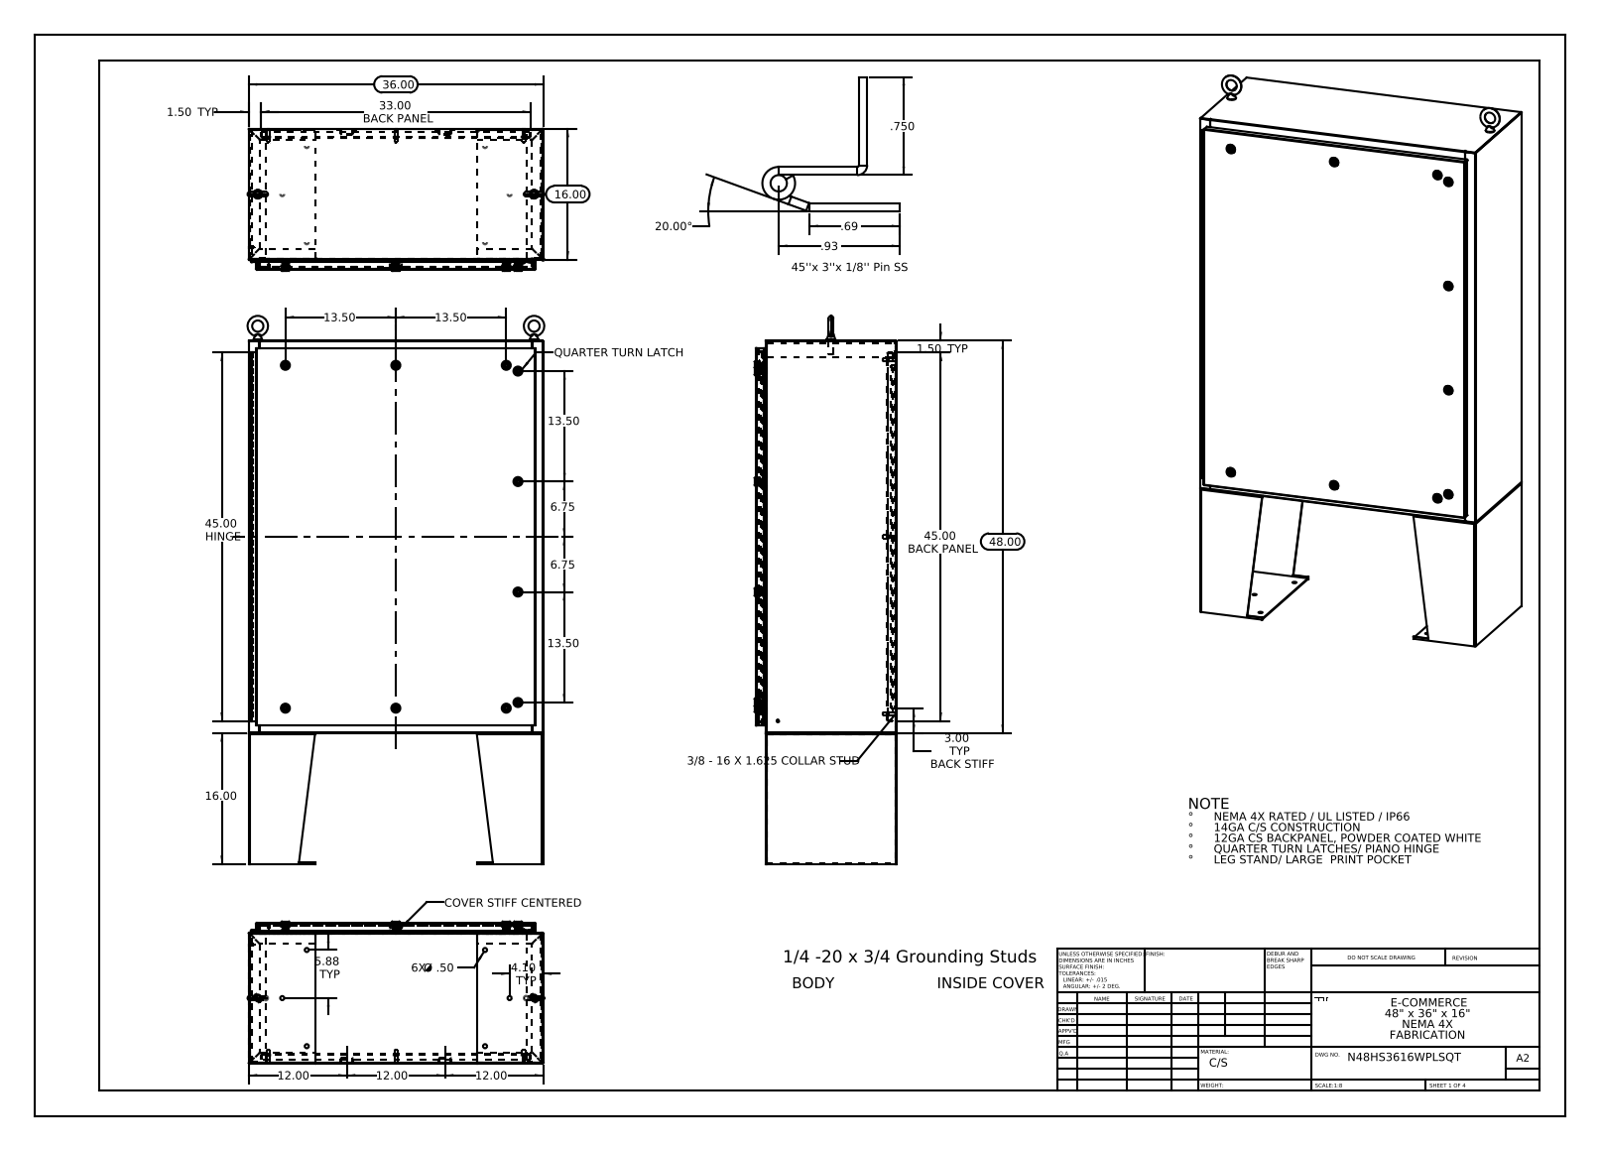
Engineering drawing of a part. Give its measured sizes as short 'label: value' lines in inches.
name: N48HS3616SSWPLSQT SD-LSK - Base; N48HS3616SSWPLSQT Hinge Enclosure Side2; N48HS3616SSWPLSQT Bottom; N48HS3616SSWPLSQT Backpanel (+8 more)
written by: SolidWorks 2013 (CONFIG_CONTROL_DESIGN)
unit: in
bodies: 34 solids, 2043 faces (1041 planar, 822 cylindrical, 180 other)
size: 67 × 36.271 × 17.201
volume: 845 in³; area: 20 263 in²
holes: 14× ⌀0.5, 6× ⌀0.25, 4× ⌀0.75, 1× ⌀0.125, 1× ⌀0.125
bosses: 10× ⌀0.625, 8× ⌀0.375, 8× ⌀0.33, 6× ⌀0.157, 6× ⌀0.14, 2× ⌀0.315, 2× ⌀0.236, 1× ⌀0.25
rounds: 36× R0.013, 30× R0.088, 10× R0.442, 8× R0.039, 8× R0.143, 6× R0.019, 4× R0.117, 4× R0.125
face distances: 0.075, 17.126, 0.104, 17.051, 1.075, 35.925, 17.201, 1, 16.126, 16.051
hole spacings: 8.393, 20, 20.123, 21.625, 25.48, 28.397, 38.003, 45.986
